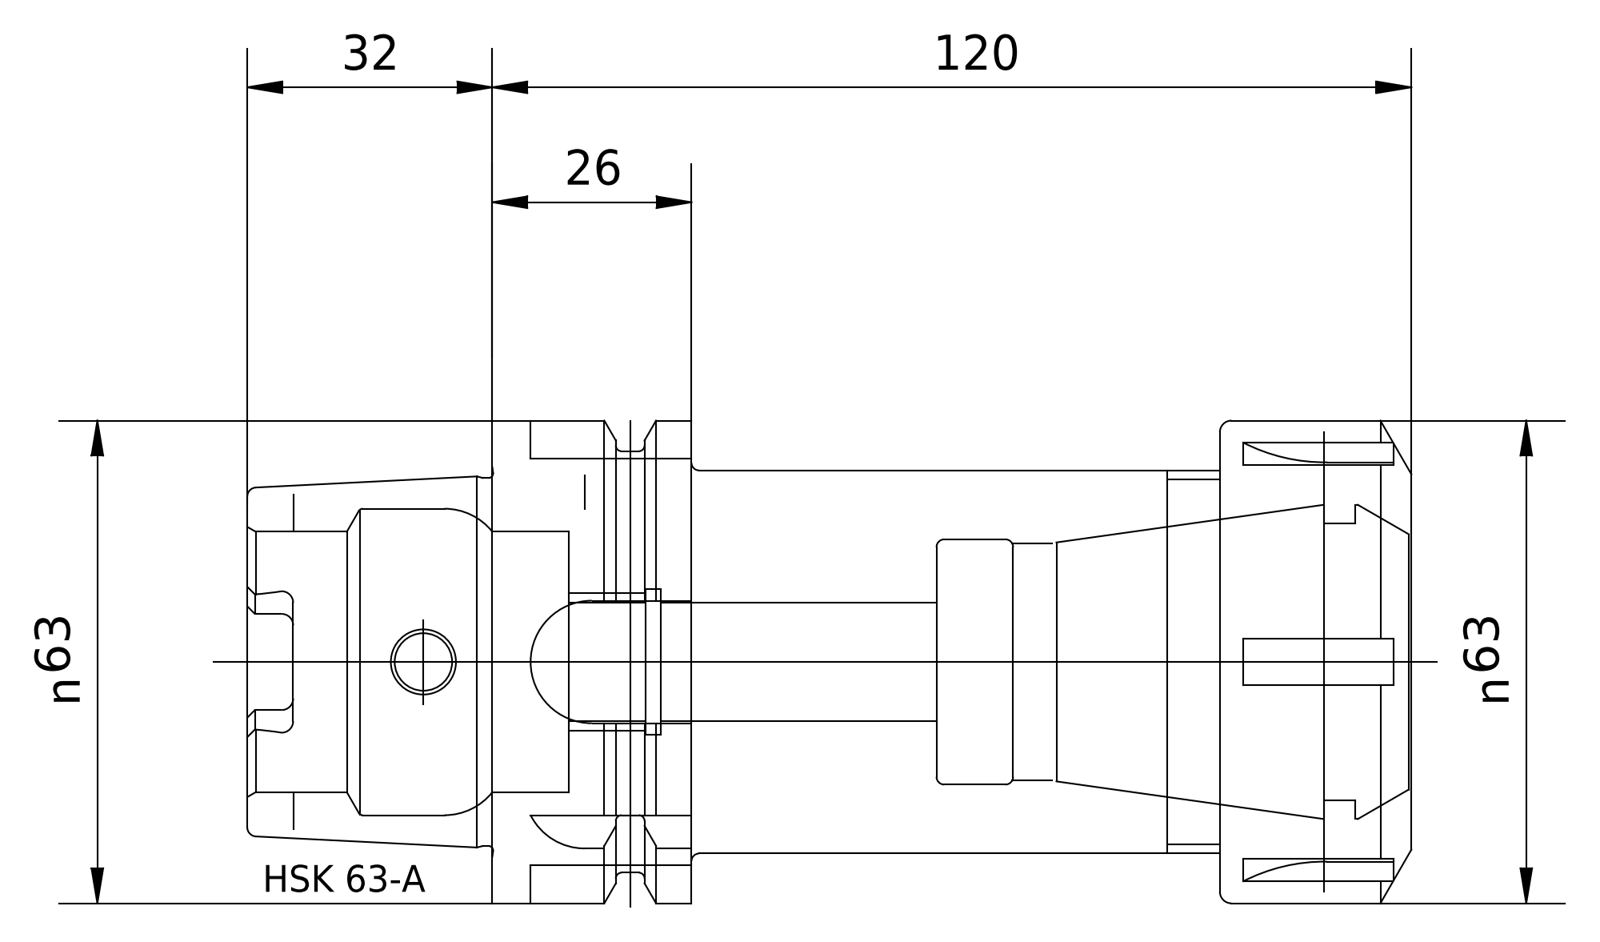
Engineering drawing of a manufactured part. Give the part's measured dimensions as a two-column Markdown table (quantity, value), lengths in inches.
| quantity | value |
| --- | --- |
| part name | A63-020-40; 83-912-40; A63-020-40_ASM |
| STEP written by | PRO/ENGINEER BY PARAMETRIC TECHNOLOGY CORPORATION, 2010430 (CONFIG_CONTROL_DESIGN) |
| units | inches |
| bodies | 2 solids, 217 faces (85 planar, 56 cylindrical, 76 other) |
| overall size | 5.984 × 2.48 × 2.48 |
| volume | 16.87 in³ |
| surface area | 76.73 in² |
| round holes (diameter × count) | 0.295 × 1, 0.394 × 1, 0.666 × 1, 0.721 × 1, 0.735 × 1, 1.201 × 1, 1.339 × 1, 1.575 × 1 |
| round bosses / shafts (diameter × count) | 2.48 × 1, 2.165 × 1, 1.969 × 1, 1.891 × 1, 0.709 × 1 |
| partial cylindrical surfaces (radius × count) | 0.059 × 6, 0.106 × 6, 0.118 × 4, 0.315 × 1, 0.316 × 1, 0.355 × 1 |
| main face-to-face distances | 1.004, 3.72, 4.724, 1.024, 2.697, 3.701, 2.638, 1.614, 1.083, 2.087 |
